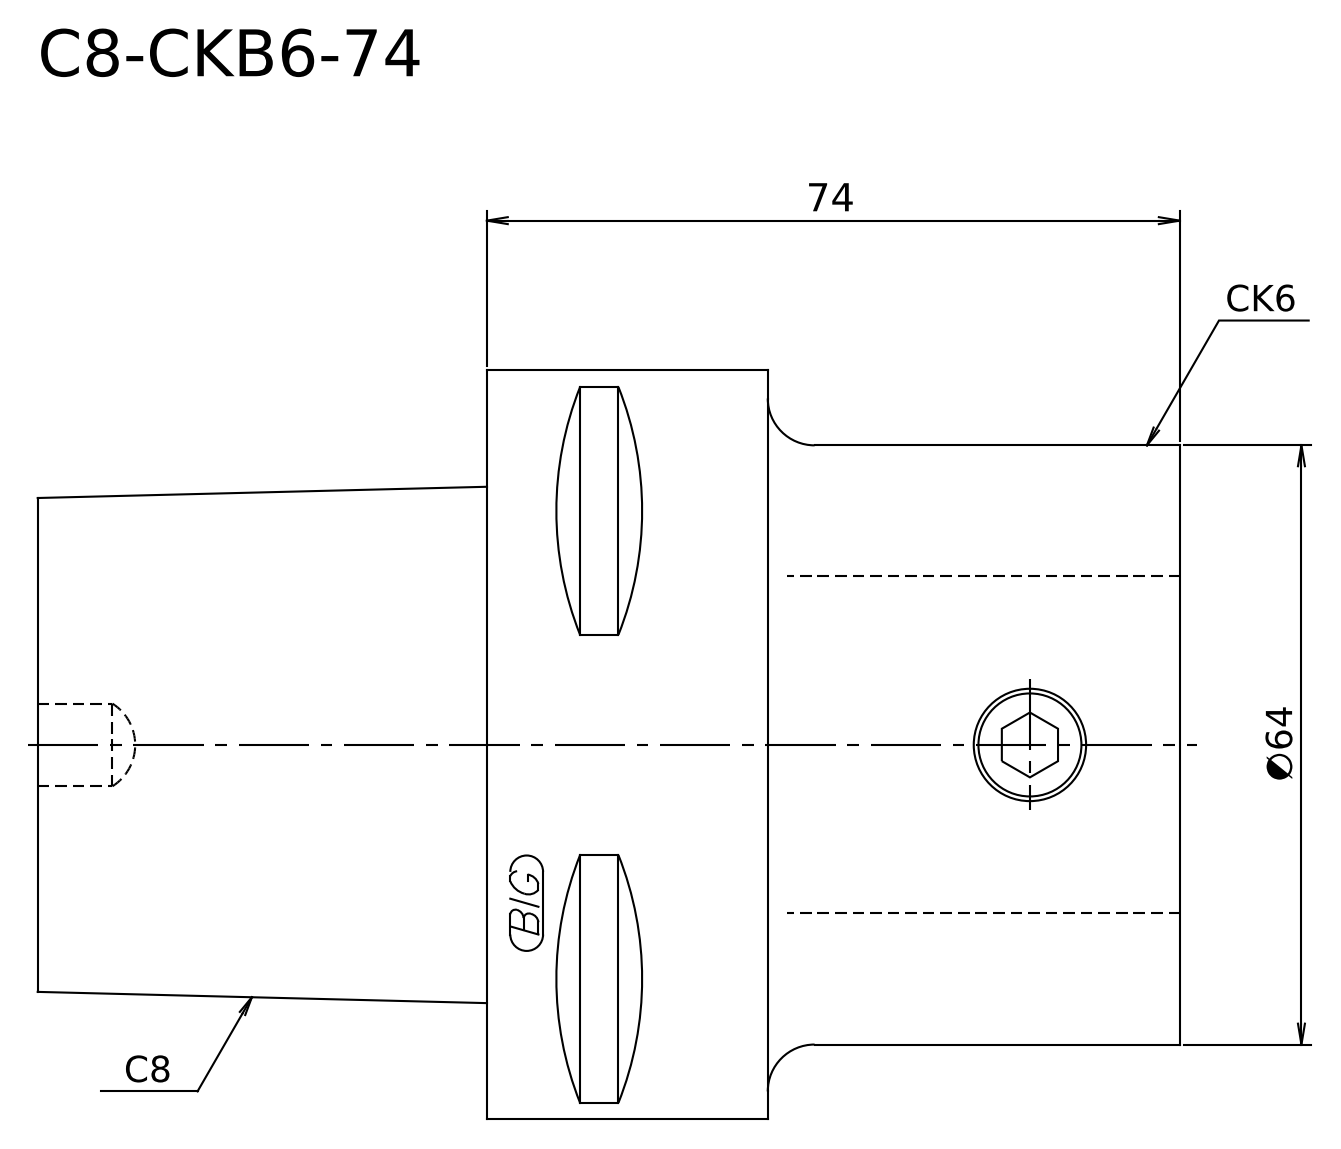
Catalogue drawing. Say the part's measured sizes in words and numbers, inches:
Its 3-D file was written by "Kubotek KeyCreator 2011 V10.0.2 (22737) (automotive_design)". It is 1 solid with 8 faces: 4 planar, 2 cylindrical and 2 other. Overall it measures 4.803 by 3.15 by 3.15 inches. Its volume is 24.49 cubic inches and its surface area 52.42 square inches. Round bosses or shafts: 1 of diameter 3.15, 1 of diameter 2.52. The main face-to-face distances are 2.913, 4.803, 1.89, 1.732, 1.181, 3.071.
